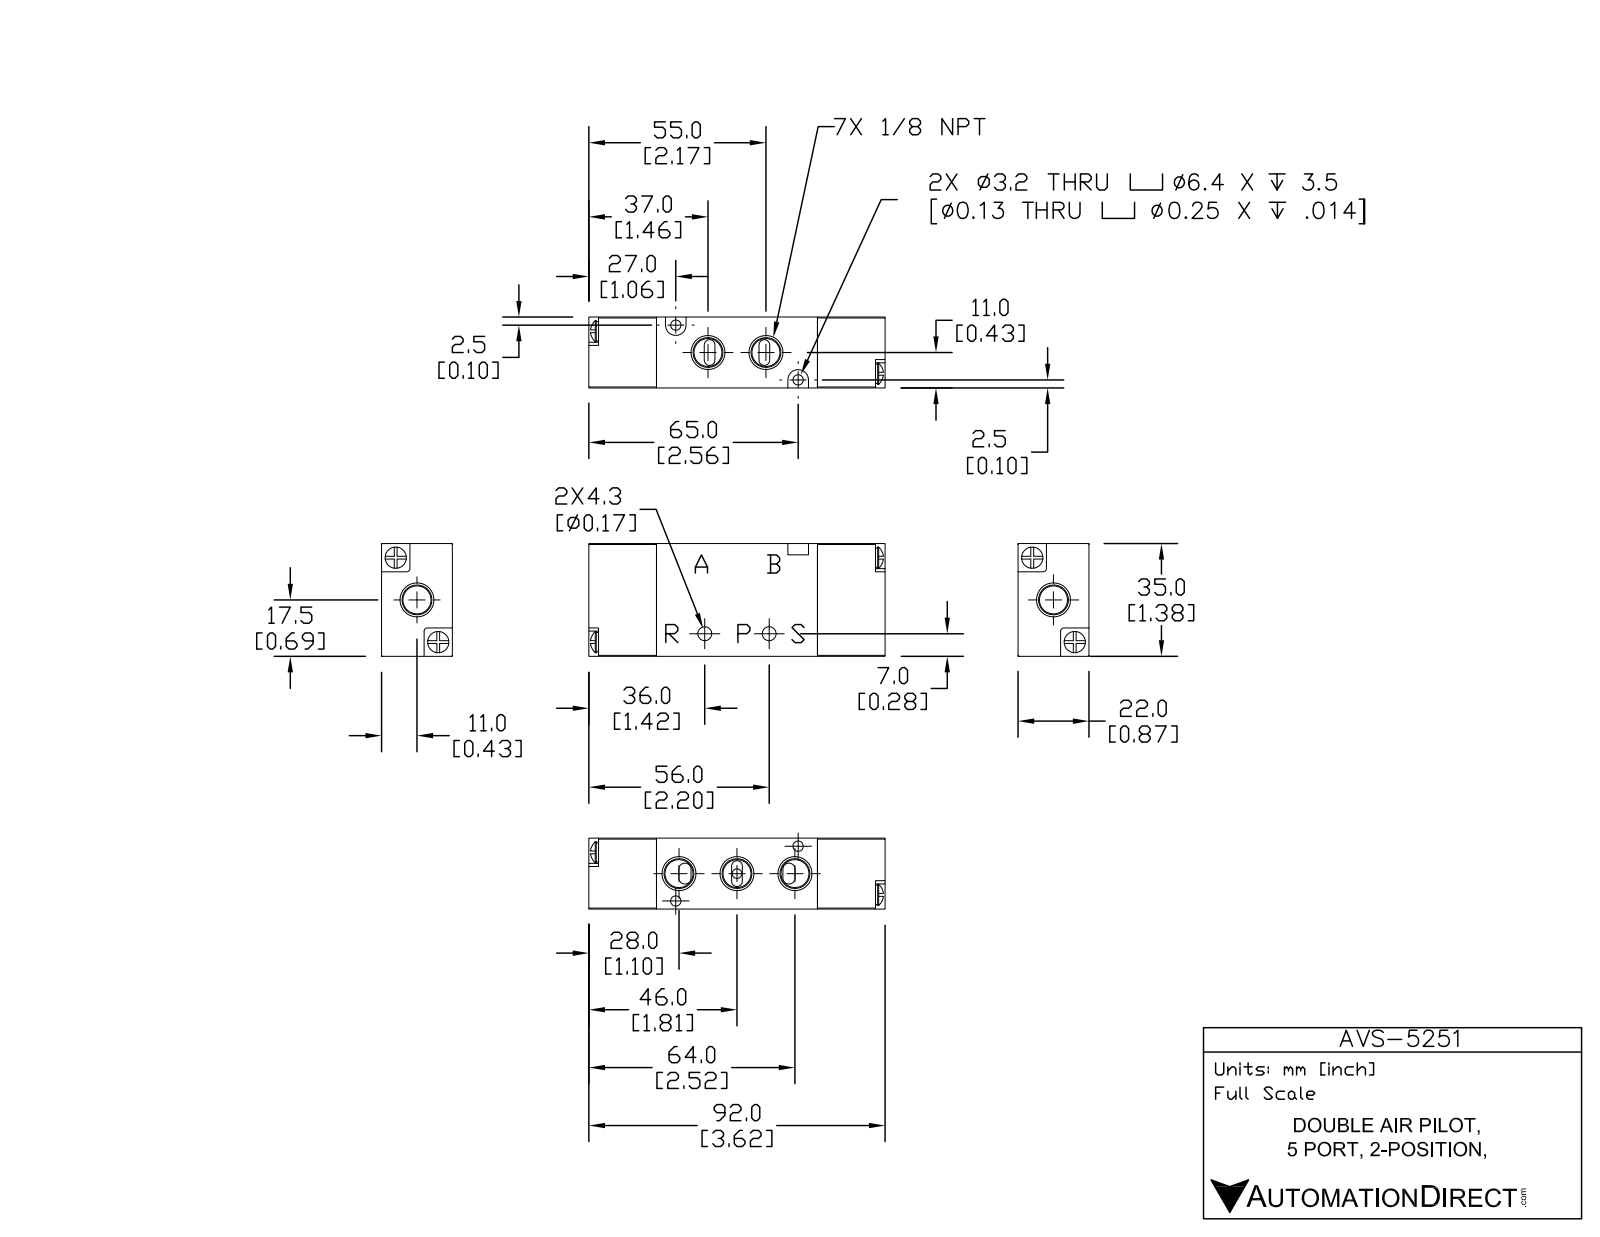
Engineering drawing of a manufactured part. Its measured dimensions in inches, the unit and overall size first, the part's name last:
Units: inches
Overall size (bounding box): 3.622 × 1.378 × 0.866
Round holes (diameter × count): ⌀0.126 ×2, ⌀0.169 ×2, ⌀0.117 ×1
Round bosses / shafts (diameter × count): ⌀0.26 ×4, ⌀0.236 ×4
Partial cylindrical surfaces — rounded edges, fillets, slot ends (radius × count): R0.065 ×6, R0.012 ×4, R0.039 ×4, R0.075 ×4, R0.126 ×2
Main face-to-face distances: 0.866, 1.378, 1.969, 0.827, 2.795, 3.622, 0.118, 3.504, 0.709, 2.677
Hole centre spacings: 0.819, 0.787, 1.639
Volume: 3.895 in³ · Surface area: 29.05 in²
Bodies: 3 solids, 199 faces (99 planar, 56 cylindrical, 44 other)
Part name (STEP PRODUCT): AVS-5251
STEP written by: SolidWorks 2015 (CONFIG_CONTROL_DESIGN)
